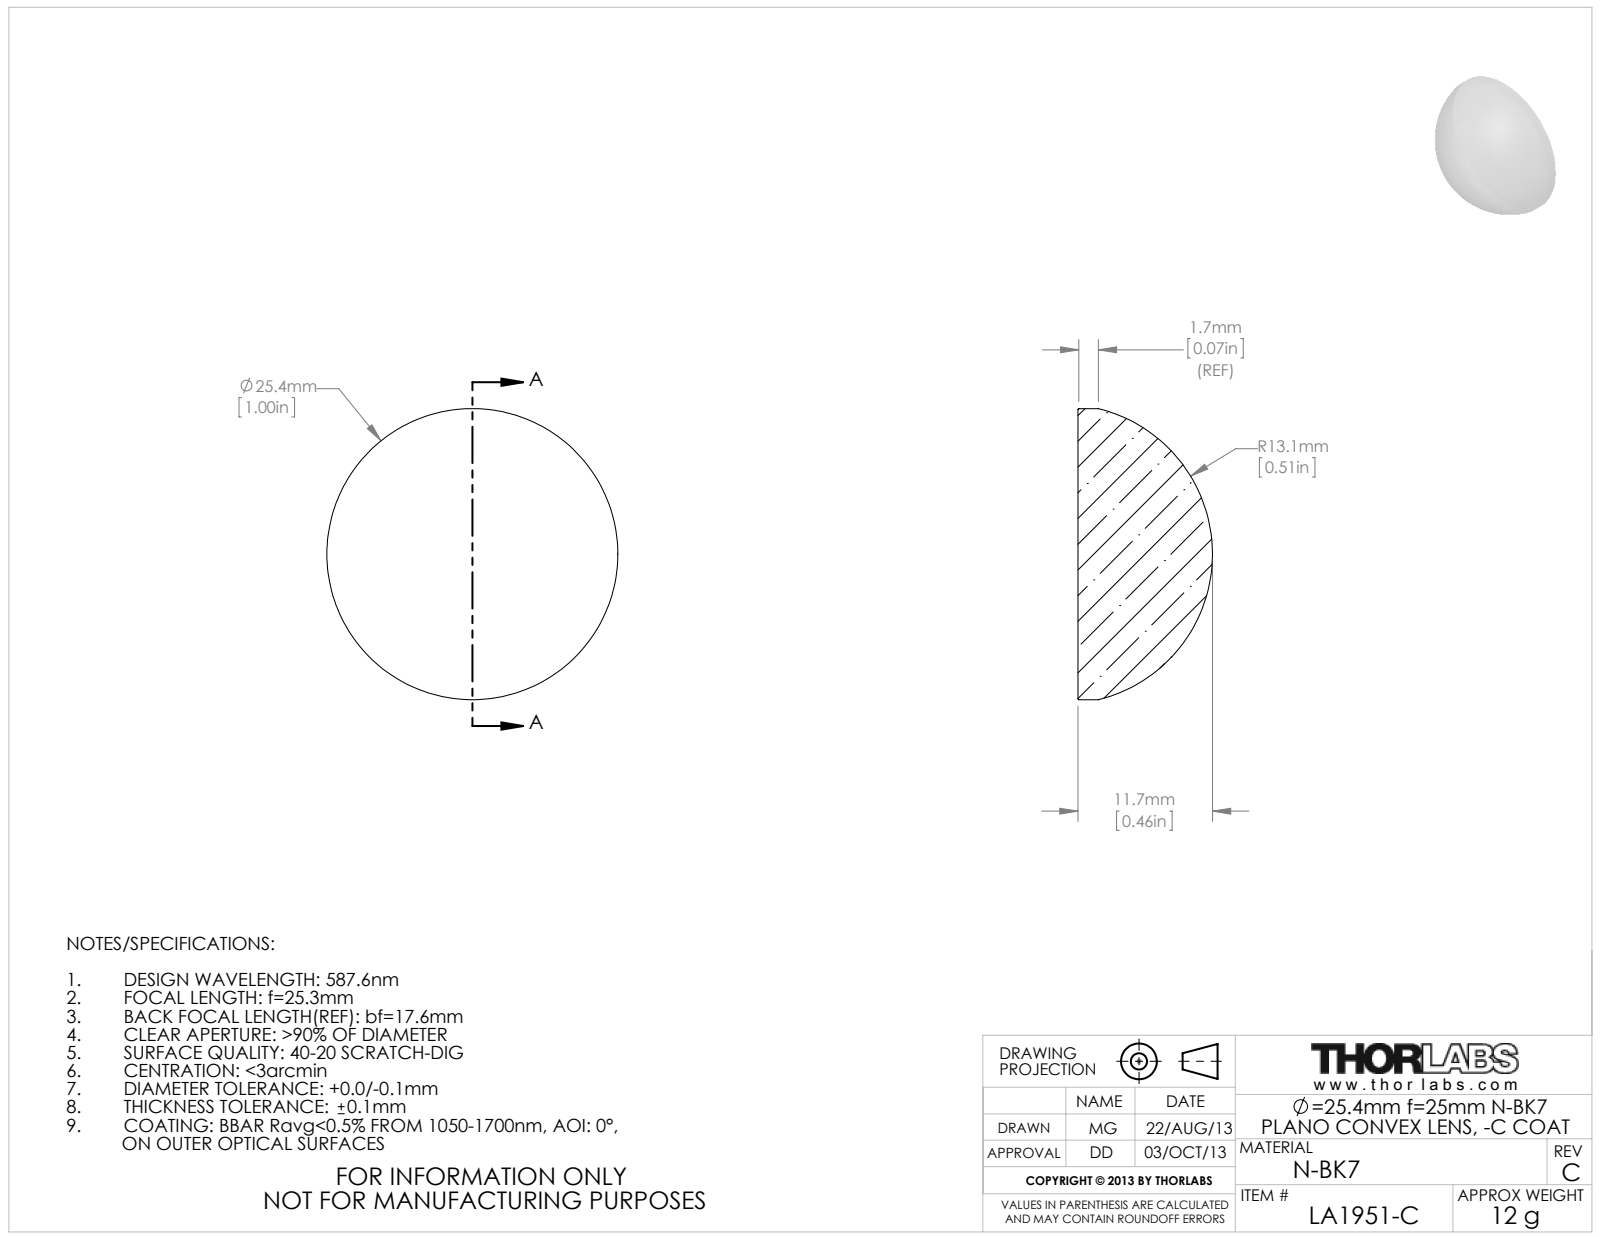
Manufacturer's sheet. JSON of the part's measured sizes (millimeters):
{"part_name": "4577-E0W", "step_written_by": "SolidWorks 2009 (AUTOMOTIVE_DESIGN)", "units": "millimeters", "bodies": {"solids": 1, "faces": 5, "planar": 1, "cylindrical": 2, "other": 2}, "overall_size": [25.4, 25.4, 11.74], "volume_mm3": 3944, "surface_area_mm2": 1467, "round_bosses_or_shafts": [[25.4, 1]]}
